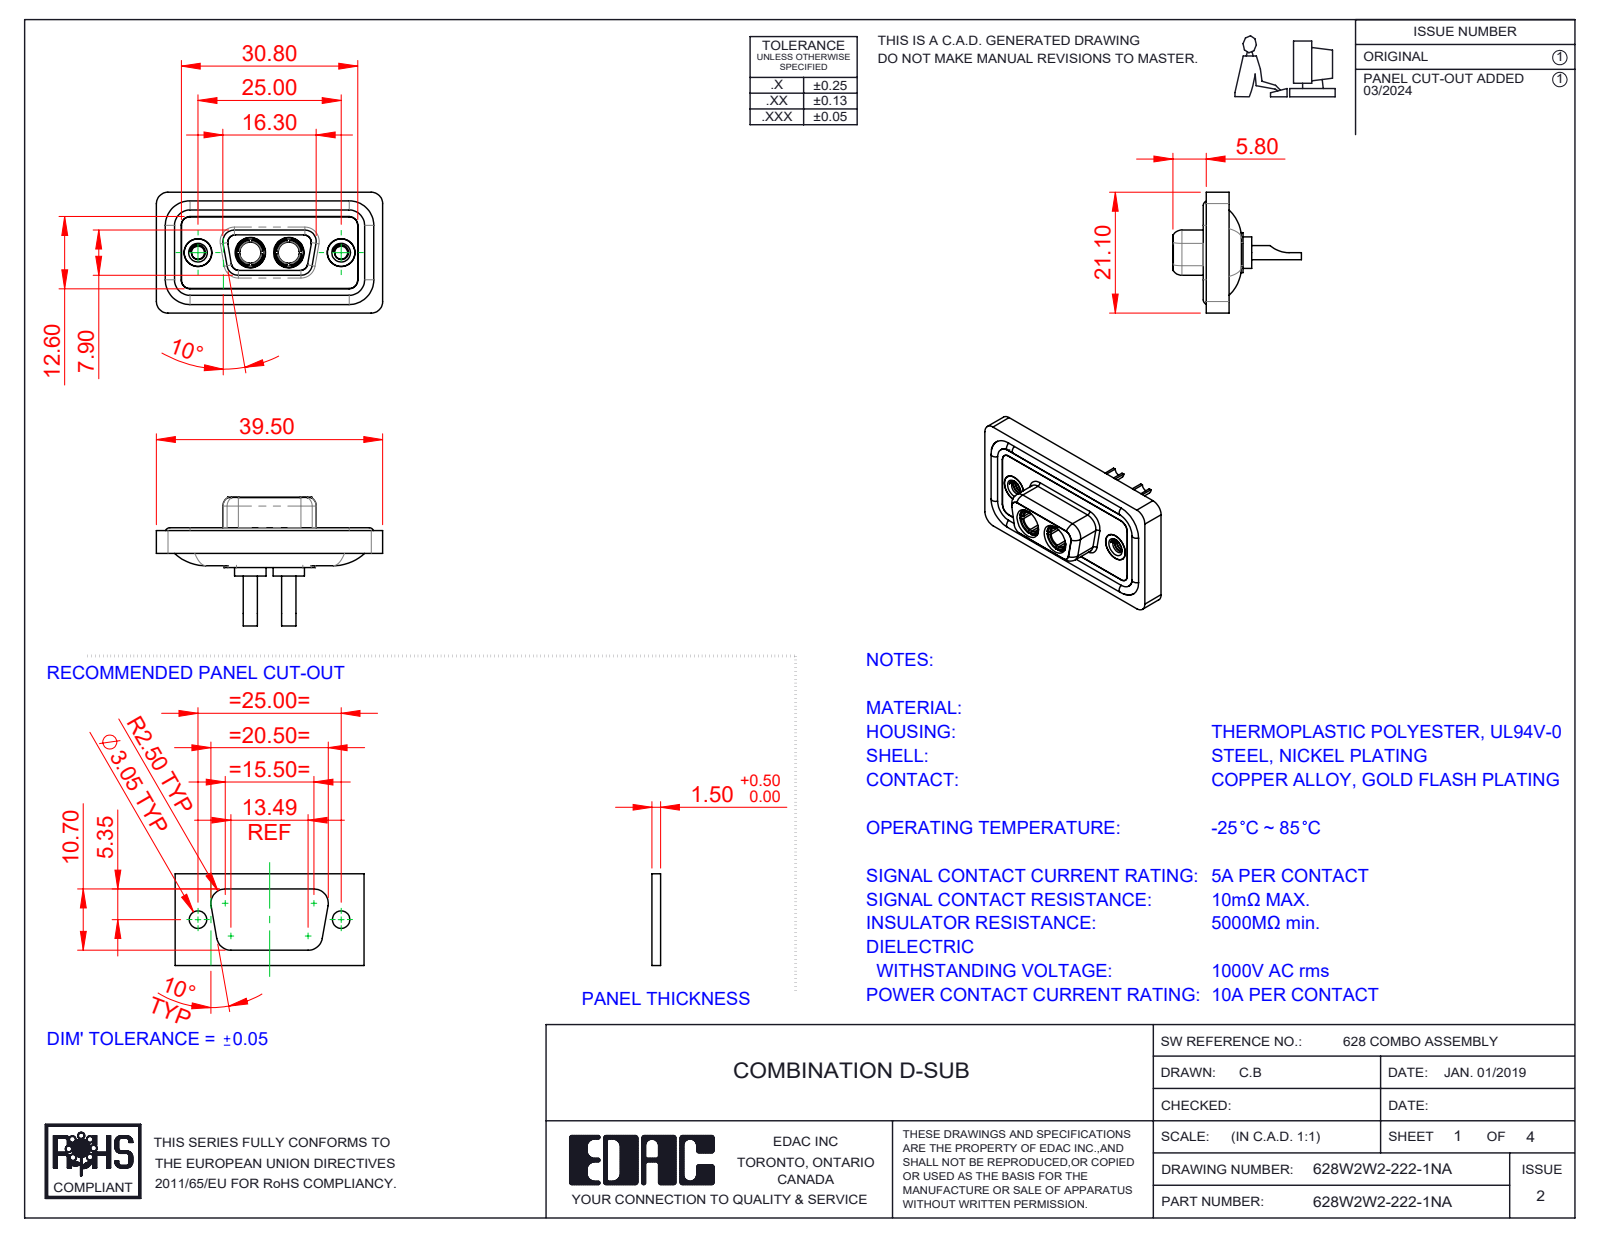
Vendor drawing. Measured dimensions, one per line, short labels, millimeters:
name: 628Combo Shell Front_09 Contacts; 628Combo Shell Rear_09 Contacts; 628Combo Waterproof Housing_09 Contacts; 628Combo Housing_2W2 (+3 more)
written by: SolidWorks 2023 (CONFIG_CONTROL_DESIGN)
unit: mm
bodies: 11 solids, 542 faces (167 planar, 242 cylindrical, 133 other)
size: 39.5 × 22.45 × 21.1
volume: 4 709 mm³; area: 7 729 mm²
holes: 4× ⌀4.85, 2× ⌀1.7, 2× ⌀2.26, 2× ⌀3.7, 2× ⌀4, 2× ⌀4.05, 2× ⌀5, 2× ⌀5.3
bosses: 4× ⌀1.6, 2× ⌀5.5, 2× ⌀5.2, 2× ⌀4.96, 2× ⌀4.95, 2× ⌀4.8, 2× ⌀4.75, 2× ⌀3.75
rounds: 22× R1.5, 18× R2, 8× R1.35, 8× R1.6, 4× R0.25, 4× R0.5, 4× R0.6, 4× R0.65
face distances: 0.4, 1.8, 1.1, 2.9, 0.5, 1.6, 5.65, 7.45, 1.5, 5.35
hole spacings: 9.14, 15.86, 6.72, 25
